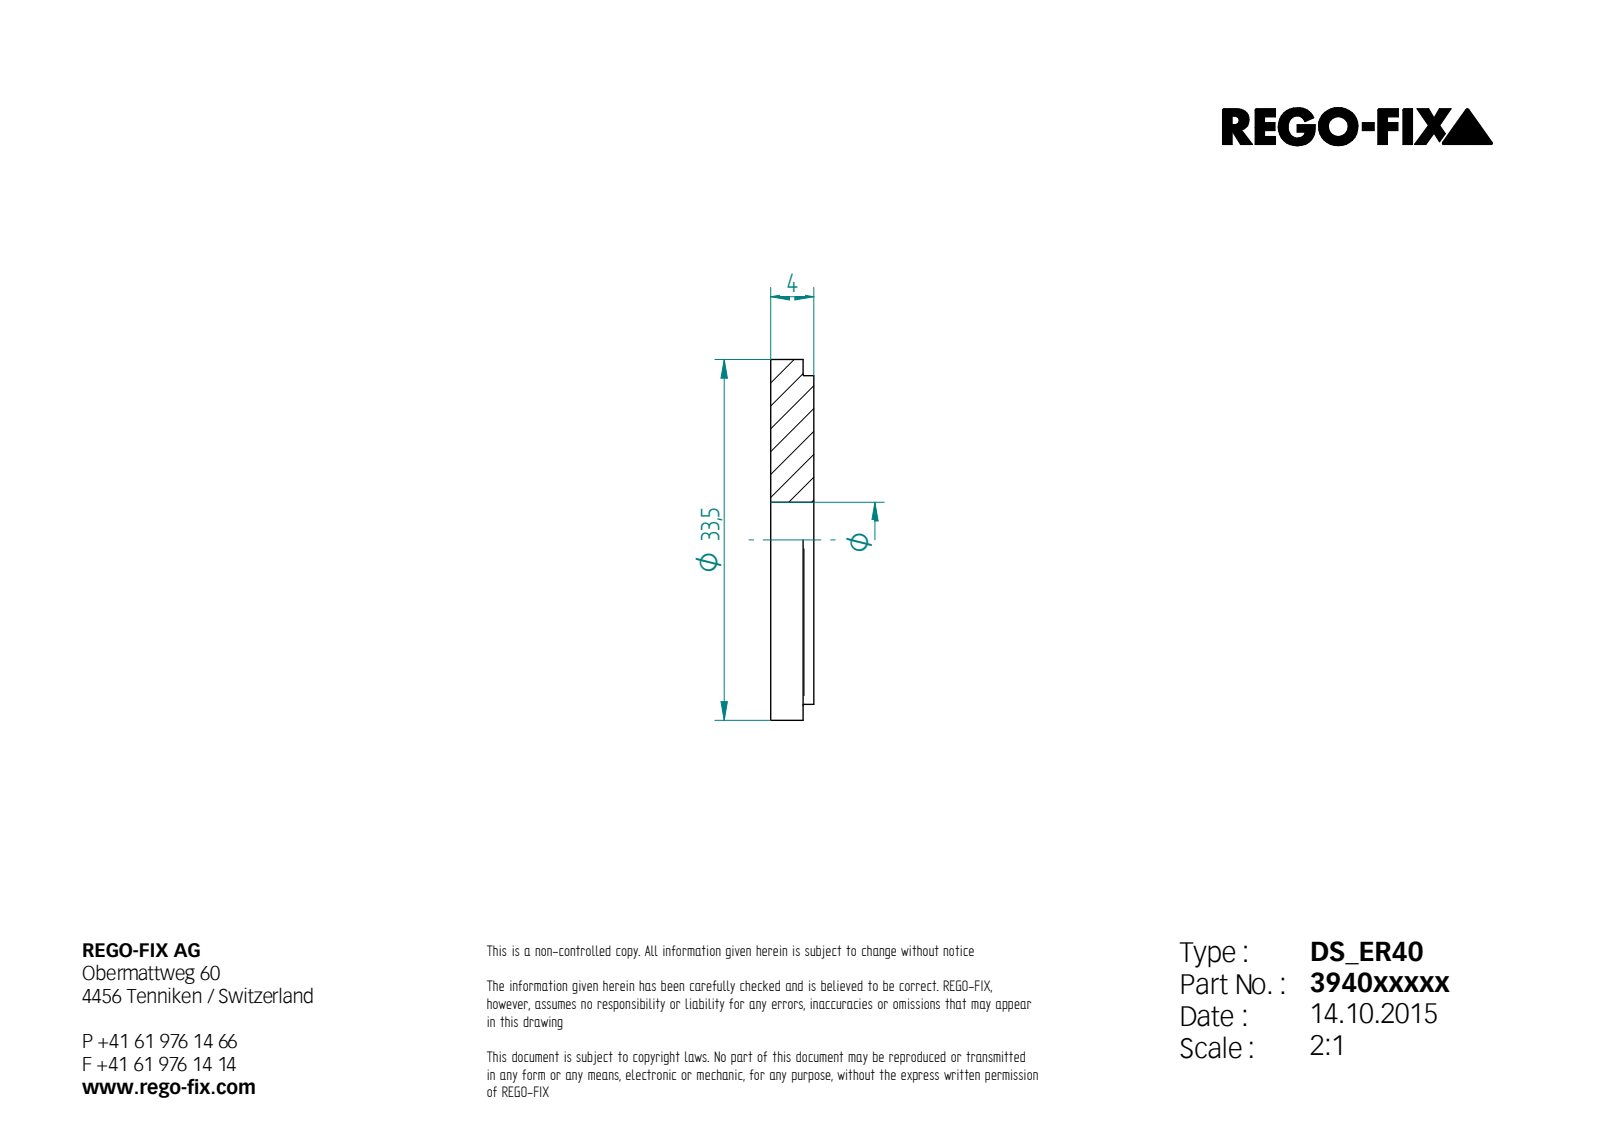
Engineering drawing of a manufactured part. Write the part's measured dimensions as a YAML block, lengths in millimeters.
part_name: "NOCUT"
step_written_by: "SIEMENS PLM Software Solid Edge ST10 (AUTOMOTIVE_DESIGN)"
units: millimeters
bodies: {solids: 1, faces: 7, planar: 3, cylindrical: 3, other: 1}
overall_size: [33.5, 33.5, 4]
volume: 3221
surface_area: 2181
round_holes:
  - {diameter: 7, count: 1}
round_bosses_or_shafts:
  - {diameter: 33.5, count: 1}
  - {diameter: 30.5, count: 1}
face_to_face_distances: [4, 1, 3]
